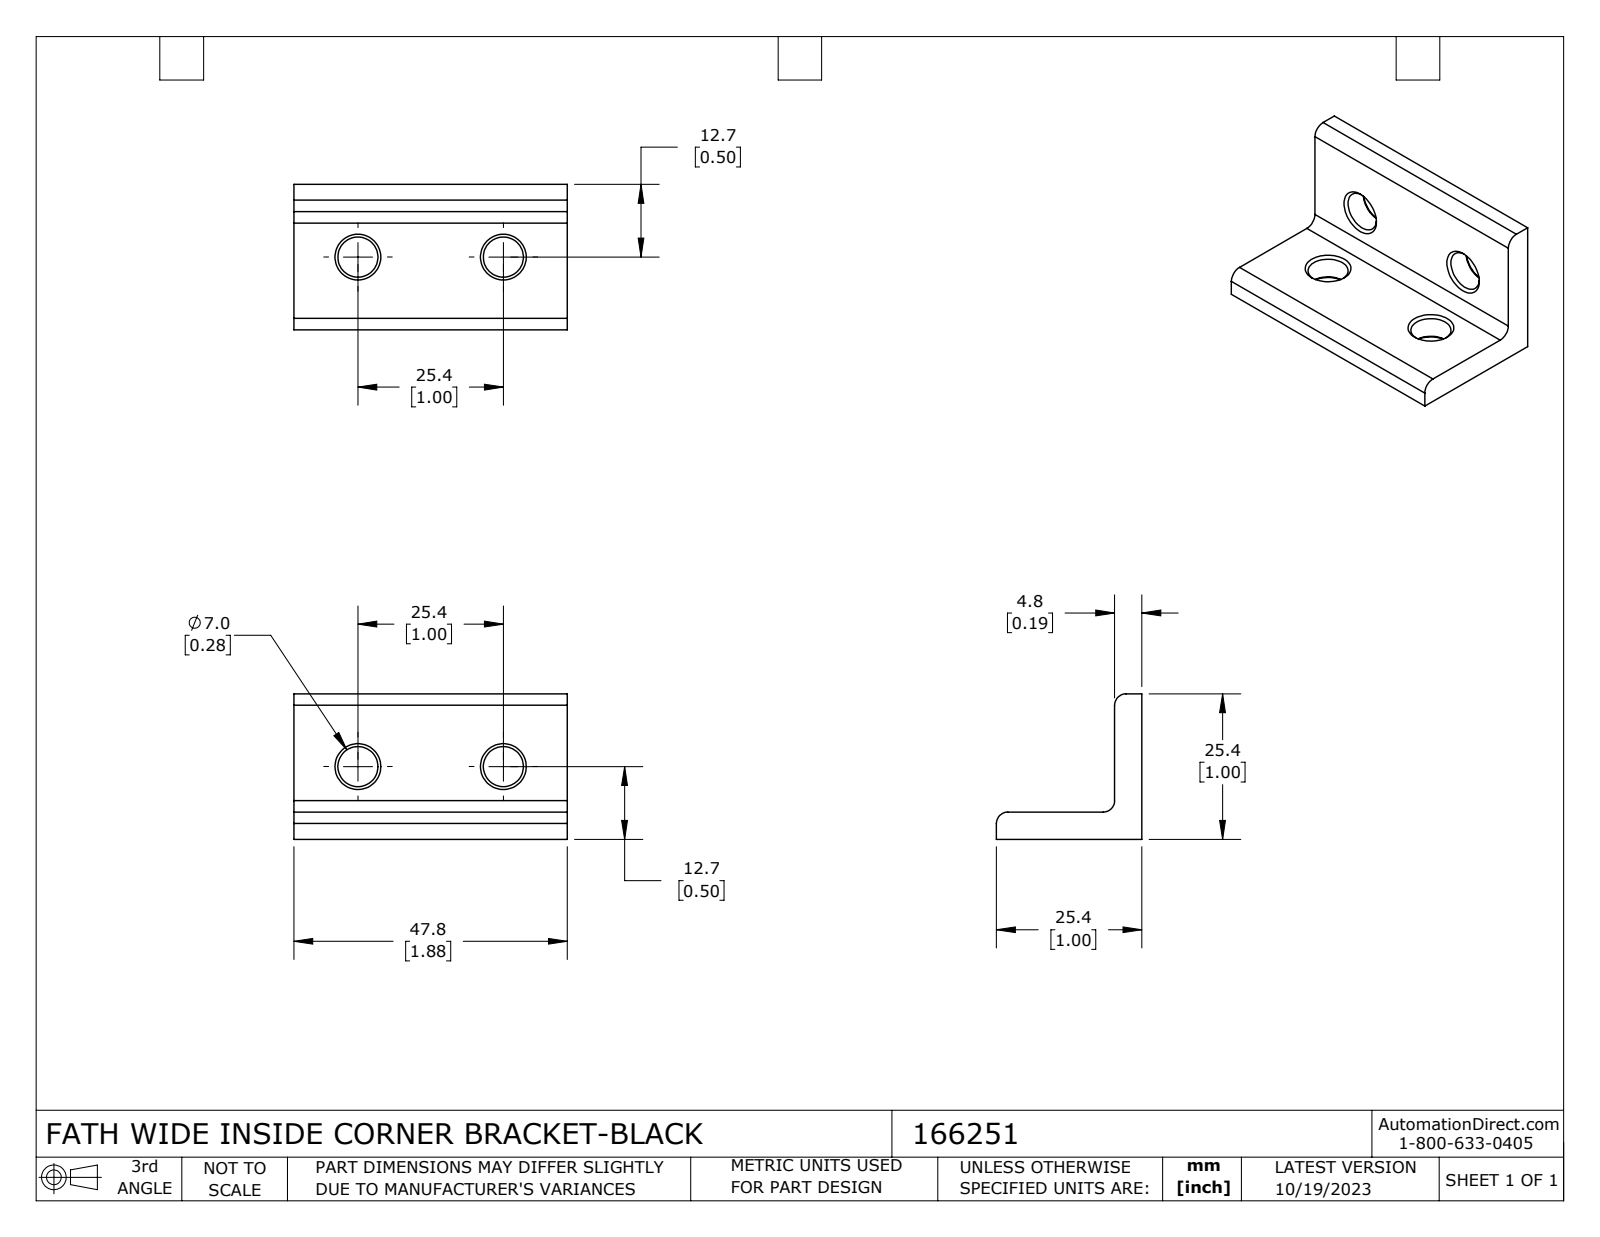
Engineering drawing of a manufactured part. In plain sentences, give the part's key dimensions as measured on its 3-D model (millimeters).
The part is named "166251". Its 3-D file was written by "SolidWorks 2023 (CONFIG_CONTROL_DESIGN)". It is 1 solid with 35 faces: 8 planar, 11 cylindrical and 16 other. Overall it measures 47.8 by 25.4 by 25.4 millimeters. Its volume is 9 670 cubic millimeters and its surface area 5 228 square millimeters. Round holes: 4 of diameter 7. Partial cylindrical surfaces (rounded edges, fillets, slot ends): 3 of radius 2. The main face-to-face distances are 4.7, 25.4, 20.7, 47.8. The hole center spacings are 25.4.
